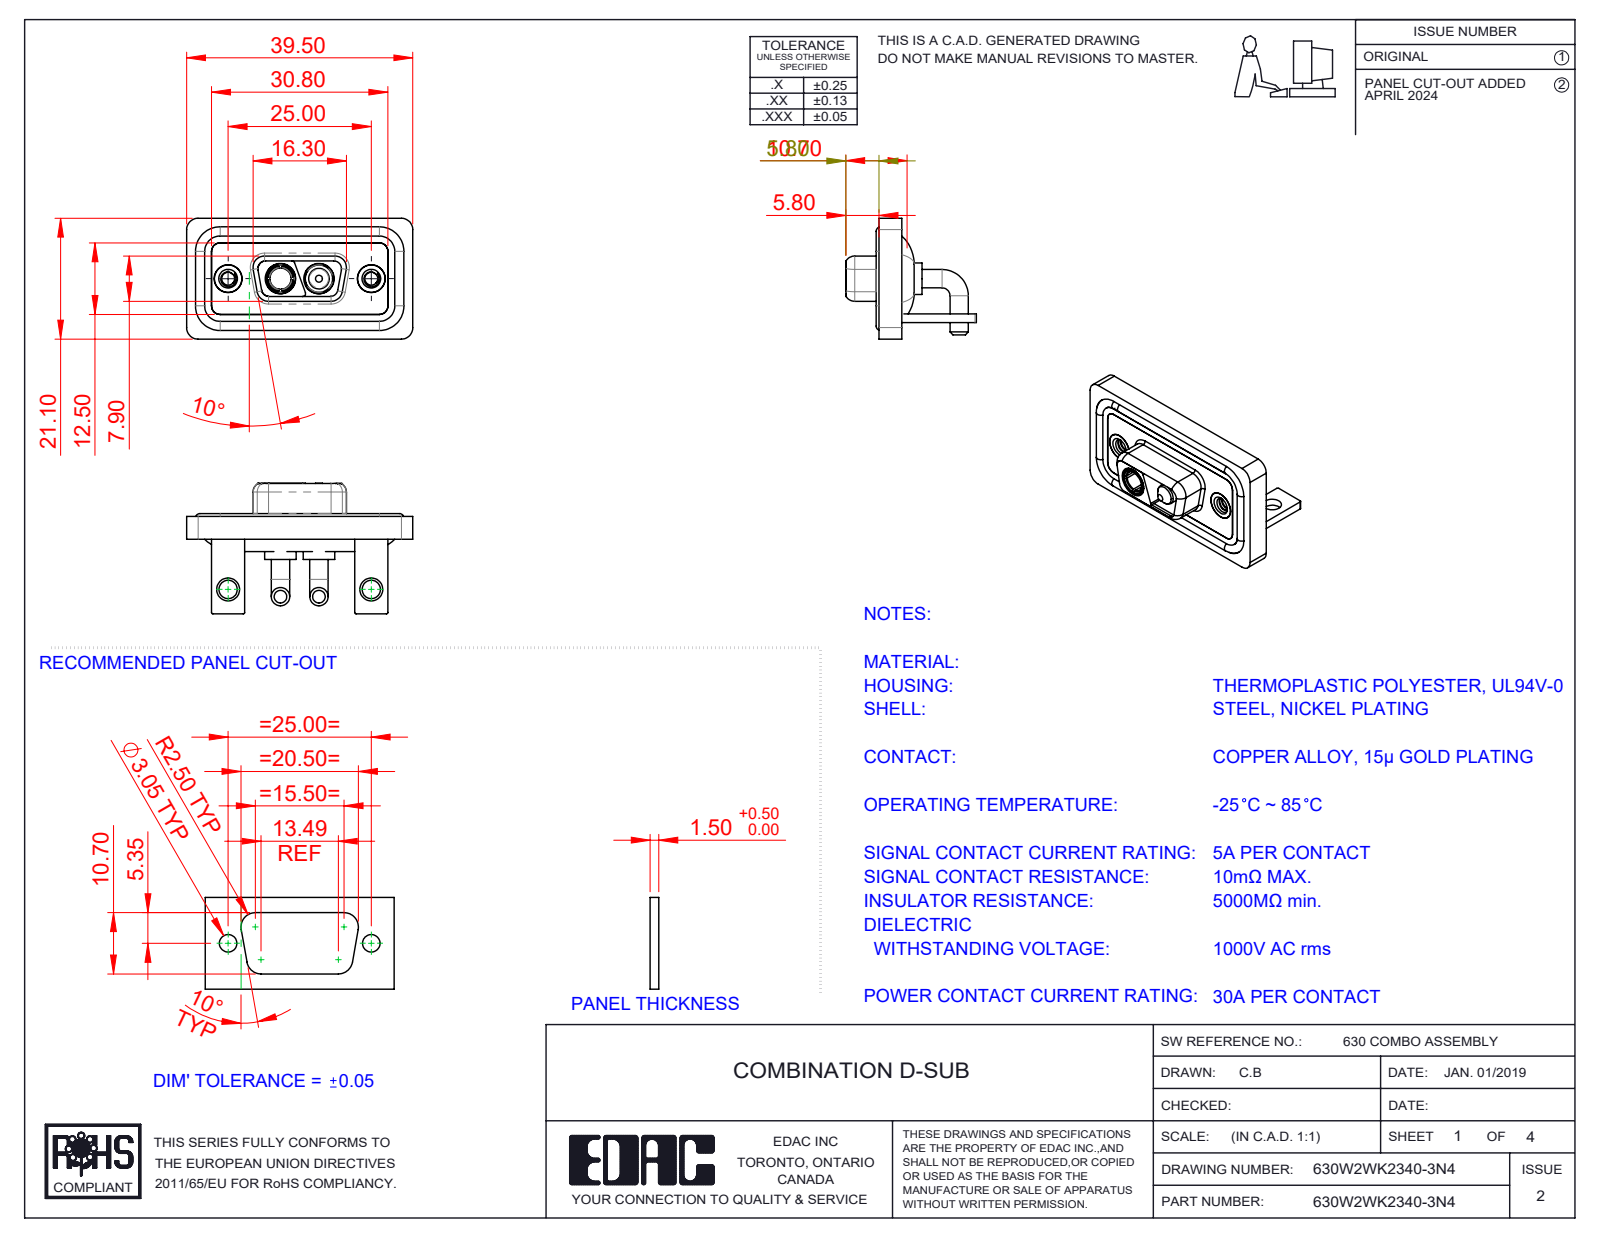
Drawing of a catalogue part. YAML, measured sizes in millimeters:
part_name: "Power Socket_30A RA; 630Combo Waterproof Housing_09 Contacts; 630Combo Housing_2WK2; 630Combo Shell Rear_09 Contacts (+5 more)"
step_written_by: "SolidWorks 2023 (CONFIG_CONTROL_DESIGN)"
units: millimeters
bodies: {solids: 13, faces: 556, planar: 164, cylindrical: 259, other: 133}
overall_size: [39.5, 22.8, 21.1]
volume: 5129
surface_area: 8266
round_holes:
  - {diameter: 4.85, count: 4}
  - {diameter: 2.26, count: 2}
  - {diameter: 3.2, count: 2}
  - {diameter: 4, count: 2}
  - {diameter: 4.05, count: 2}
  - {diameter: 5, count: 2}
  - {diameter: 5.3, count: 2}
  - {diameter: 3.7, count: 1}
round_bosses_or_shafts:
  - {diameter: 3.2, count: 4}
  - {diameter: 1.6, count: 4}
  - {diameter: 5.5, count: 2}
  - {diameter: 5.2, count: 2}
  - {diameter: 4.95, count: 2}
  - {diameter: 4.8, count: 2}
  - {diameter: 4.75, count: 2}
  - {diameter: 3.75, count: 2}
partial_cylinders:
  - {radius: 2, count: 19}
  - {radius: 1.5, count: 18}
  - {radius: 0.25, count: 16}
  - {radius: 1.35, count: 8}
  - {radius: 1.6, count: 8}
  - {radius: 0.5, count: 7}
  - {radius: 0.6, count: 4}
  - {radius: 0.65, count: 4}
face_to_face_distances: [0.4, 2.9, 1.5, 1.1, 3.7, 1.8, 0.8, 2.5, 1.6, 3.1]
hole_center_spacings: [9.14, 15.86, 25, 6.72]
